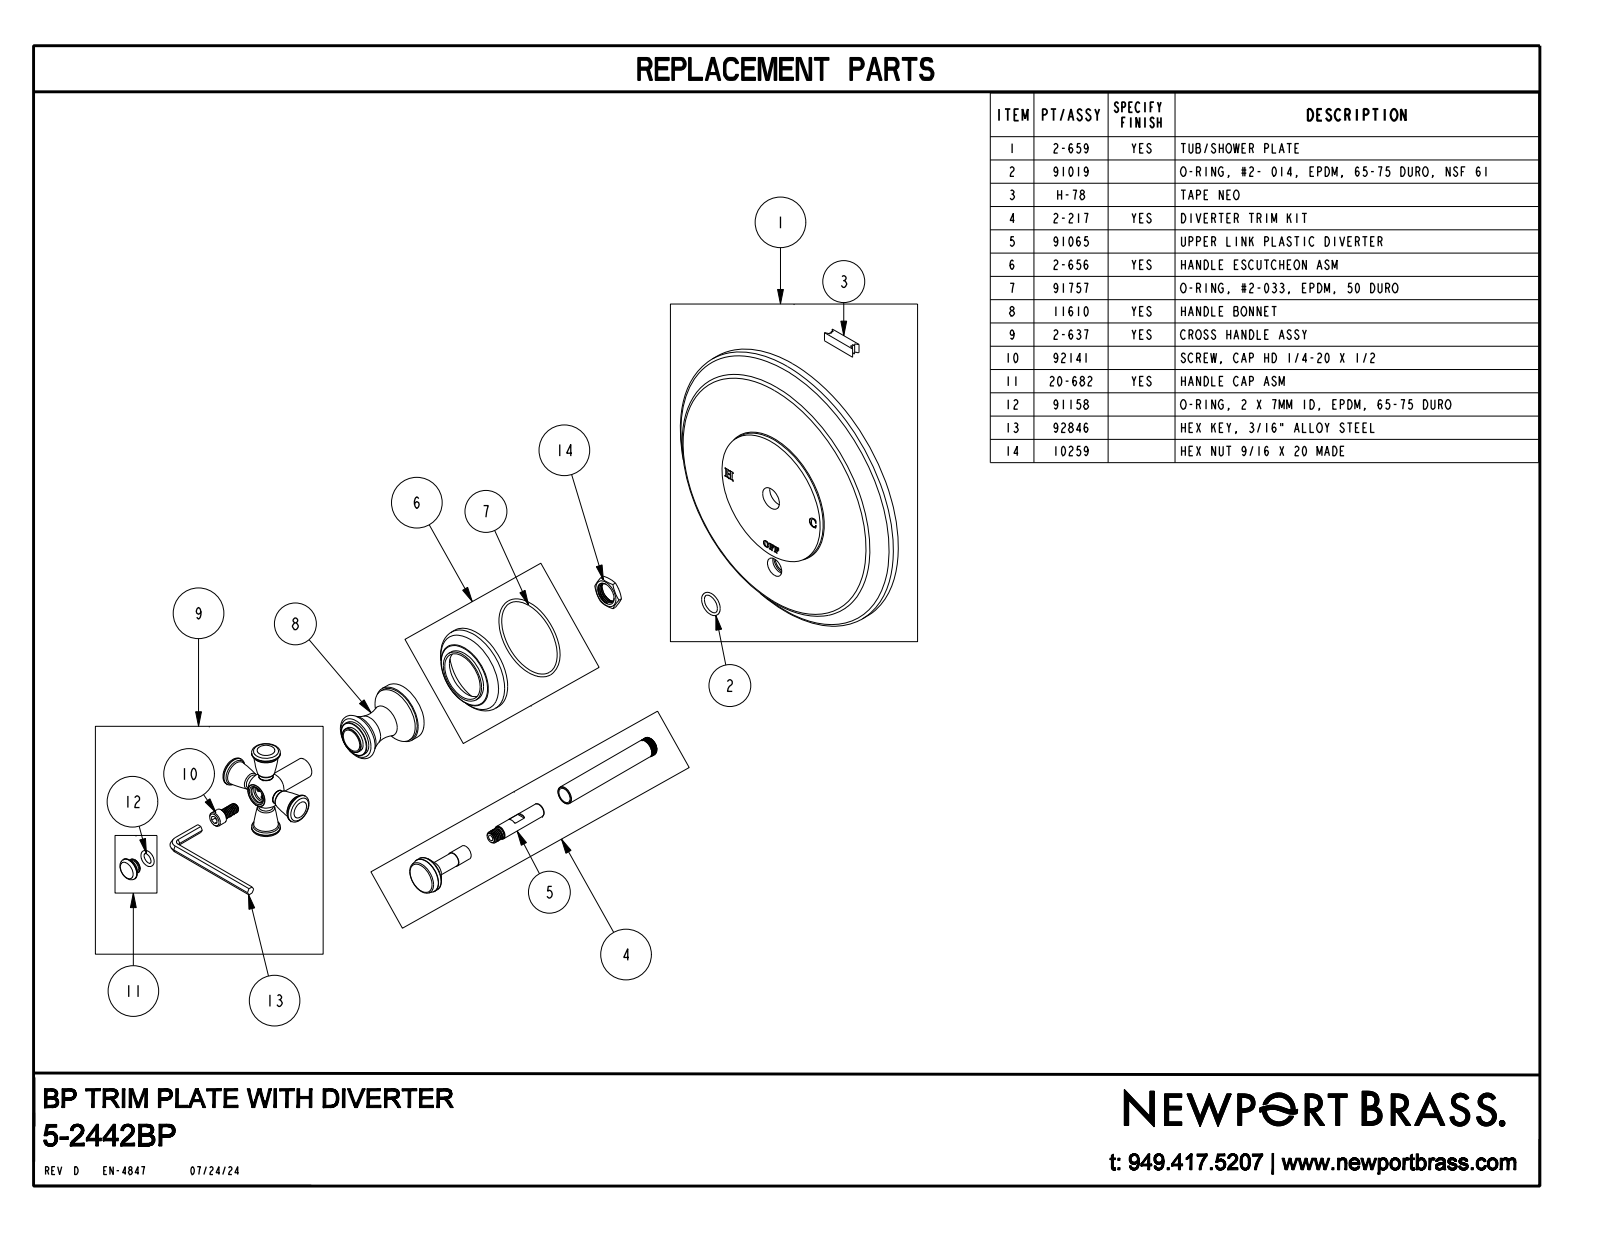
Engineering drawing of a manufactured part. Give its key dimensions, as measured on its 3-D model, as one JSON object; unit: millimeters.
{"part_name": "5-2442BP", "step_written_by": "CREO PARAMETRIC BY PTC INC, 2018400 (CONFIG_CONTROL_DESIGN)", "units": "millimeters", "bodies": {"solids": 1, "faces": 294, "planar": 45, "cylindrical": 38, "other": 211}, "overall_size": [190.5, 190.5, 103.1], "volume_mm3": 494900, "surface_area_mm2": 76260, "round_bosses_or_shafts": [[22.9, 2], [18.3, 2], [9.1, 2], [190.5, 1], [55.9, 1], [37.8, 1], [36.1, 1], [16.8, 1]], "face_to_face_distances": [15.9, 19.1, 3.2, 50.2, 34.3, 31.2, 30, 14.1, 10.9, 20.2]}
